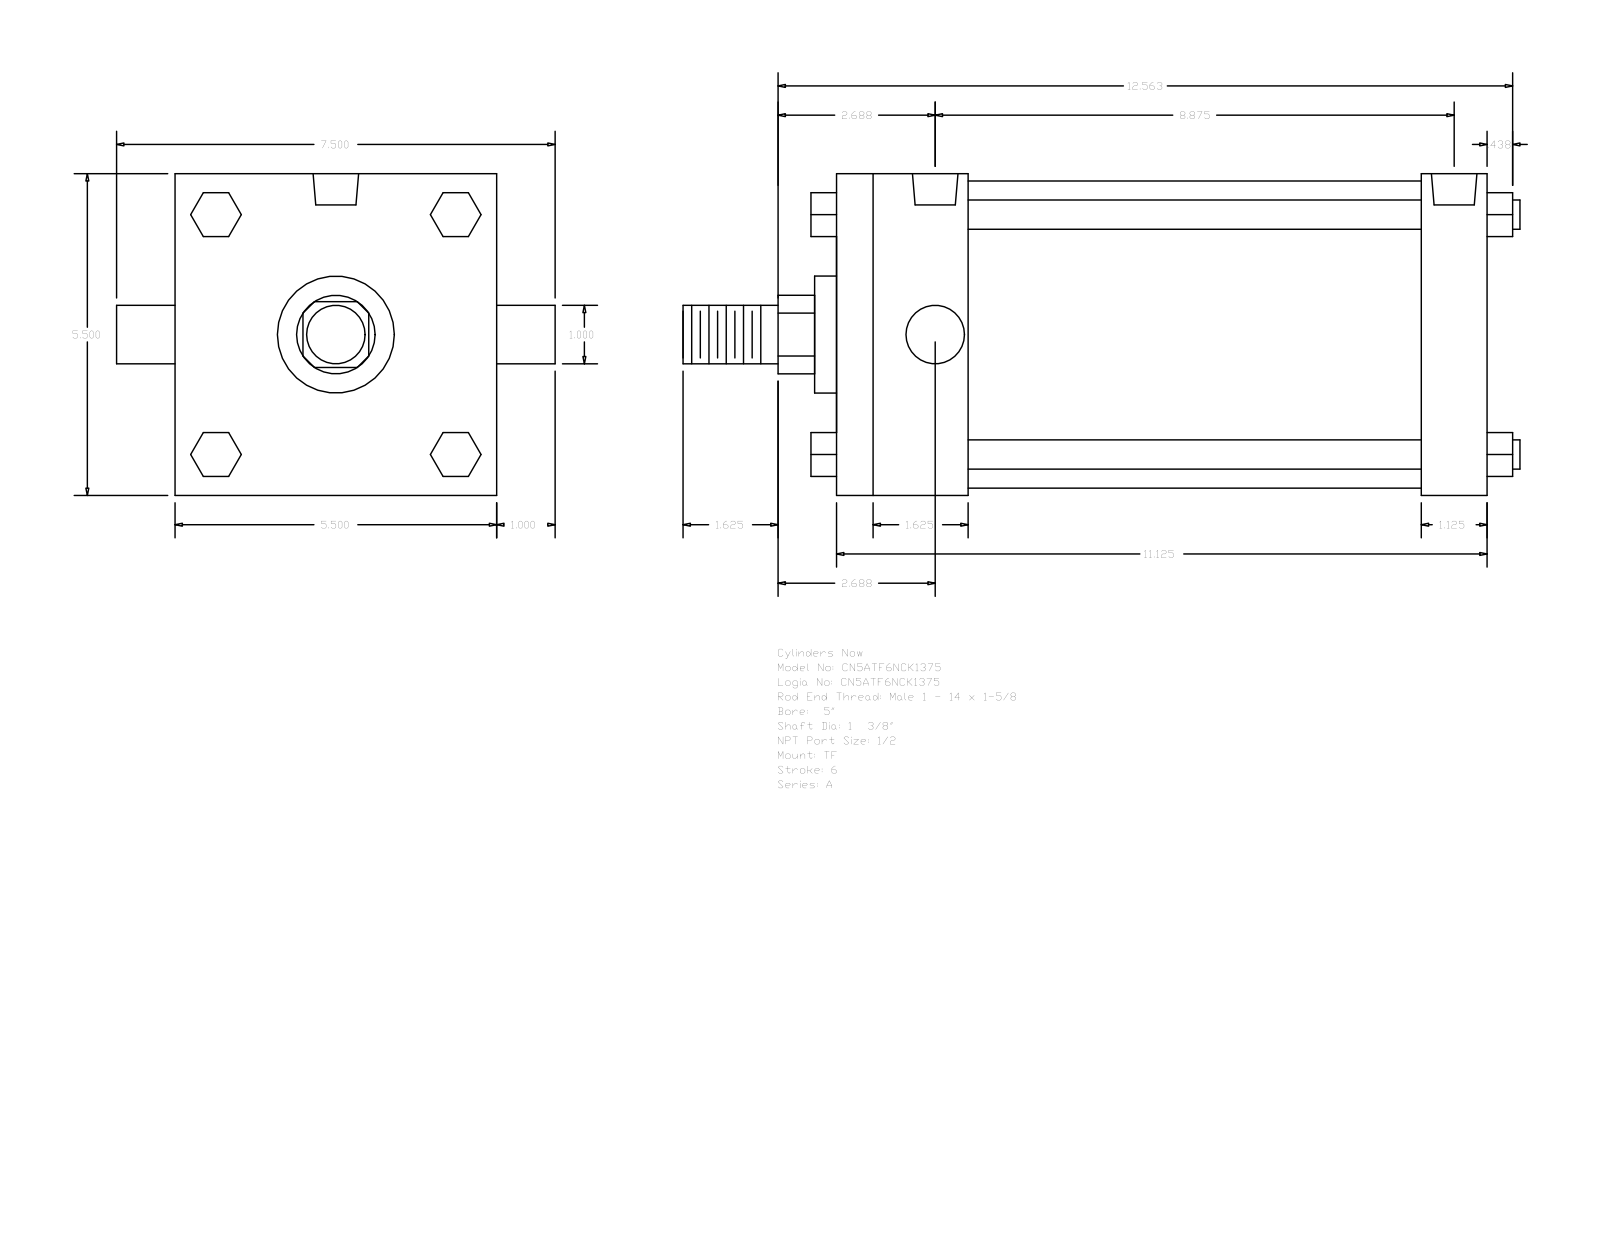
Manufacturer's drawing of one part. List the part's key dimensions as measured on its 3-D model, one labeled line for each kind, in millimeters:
Part name (STEP PRODUCT): A_TF__0500_1.375
STEP written by: GSSL Pune (CONFIG_CONTROL_DESIGN)
Units: millimetres
Bodies: 0 solids, 120 faces (92 planar, 28 cylindrical, 0 other)
Overall size (bounding box): 363.54 × 190.5 × 139.7
Round holes (diameter × count): ⌀8.73 ×3, ⌀19.77 ×2
Round bosses / shafts (diameter × count): ⌀12.7 ×4, ⌀25.4 ×2, ⌀133.35 ×1, ⌀50.8 ×1, ⌀34.92 ×1
Partial cylindrical surfaces — rounded edges, fillets, slot ends (radius × count): R17.06 ×1
Main face-to-face distances: 139.7, 282.58, 57.15, 28.58, 254, 196.85, 225.43, 19.05, 52.07, 90.18
Hole centre spacings: 2.39, 223.04, 220.65, 225.43
